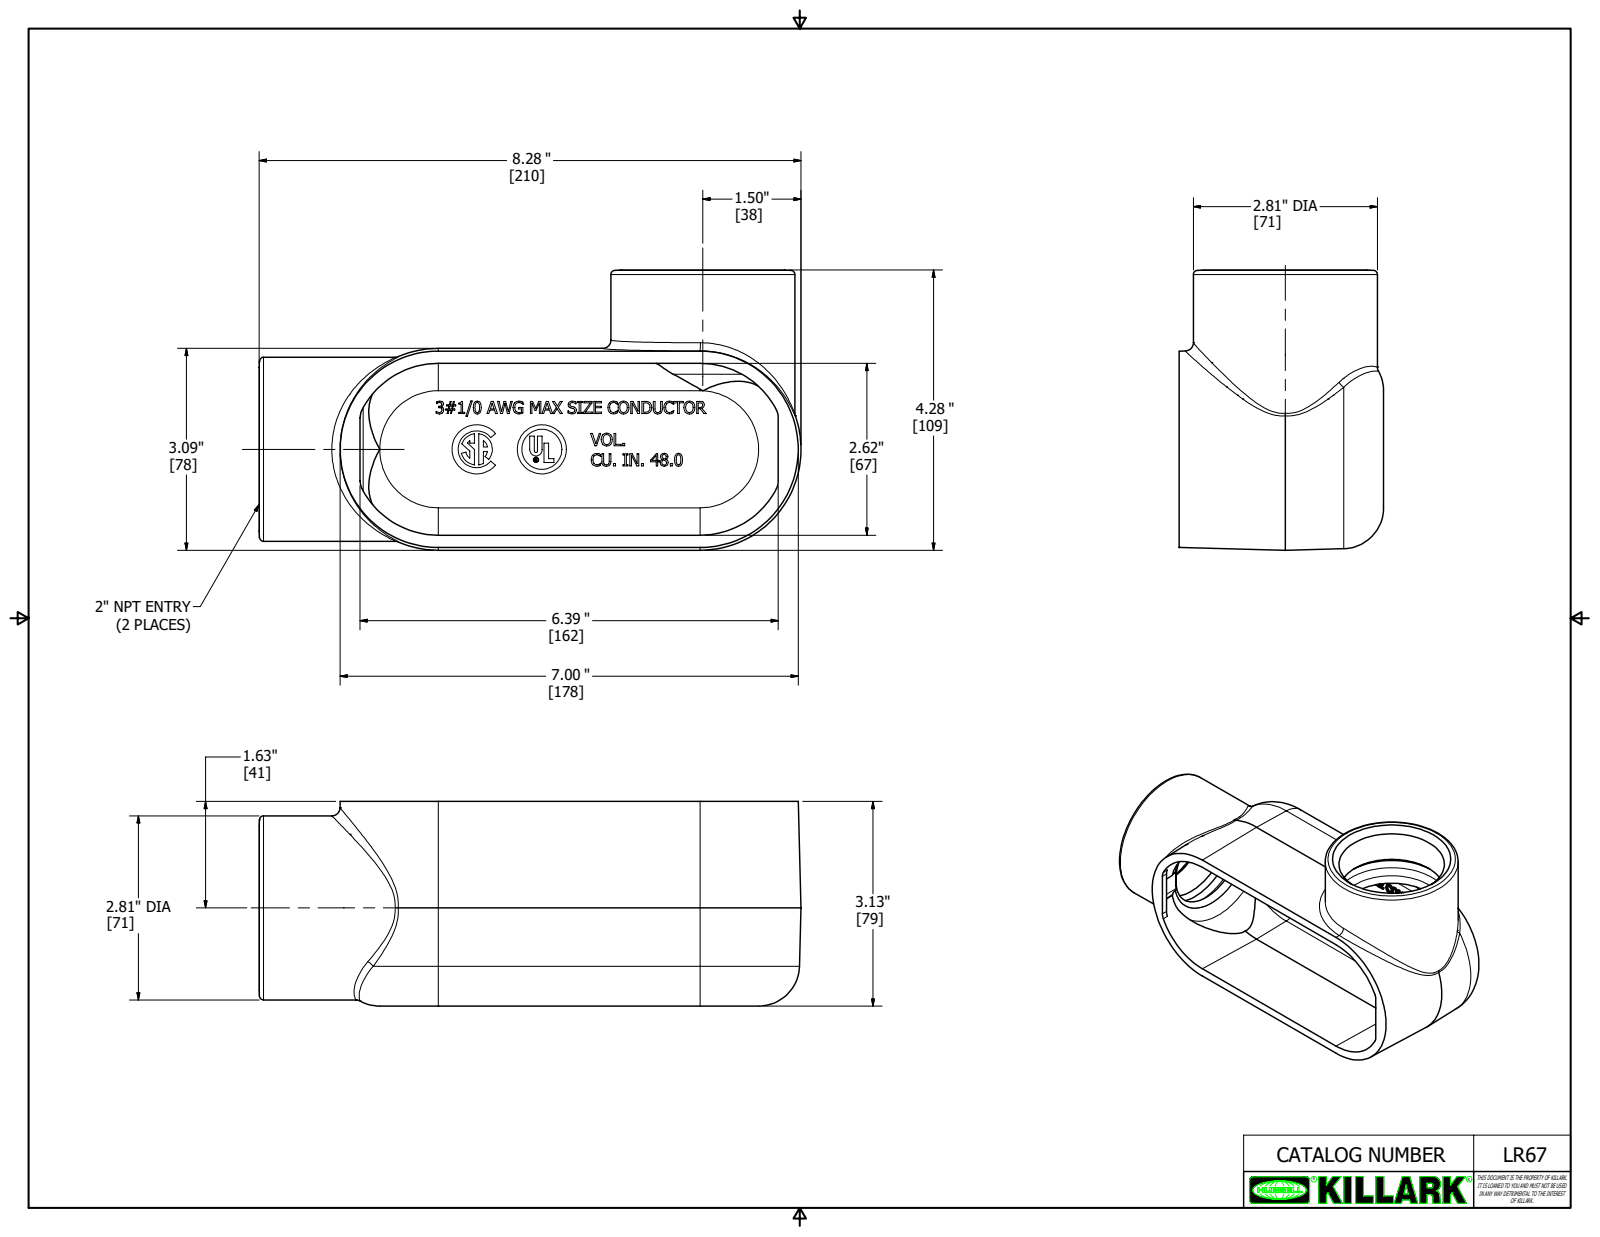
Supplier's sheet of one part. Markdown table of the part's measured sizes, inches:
| quantity | value |
| --- | --- |
| part name | 17710-2 |
| STEP written by | Autodesk Inventor 2018 (AUTOMOTIVE_DESIGN) |
| units | inches |
| bodies | 1 solid, 855 faces (524 planar, 36 cylindrical, 295 other) |
| overall size | 8.281 × 4.281 × 3.125 |
| volume | 16.48 in³ |
| surface area | 170 in² |
| round holes (diameter × count) | 2.381 × 2, 0.07 × 1, 0.611 × 1, 2.625 × 1 |
| round bosses / shafts (diameter × count) | 2.812 × 2, 0.75 × 1, 0.083 × 1 |
| partial cylindrical surfaces (radius × count) | 0.05 × 4, 0.125 × 4, 0.437 × 2, 0.625 × 2, 0.008 × 1, 0.013 × 1, 0.024 × 1, 0.094 × 1 |
| main face-to-face distances | 0.187, 2.898, 2.71, 3.085, 3.125, 2.937, 0.188, 0.219, 0.031, 2.906 |
| hole center spacings | 0.183 |
